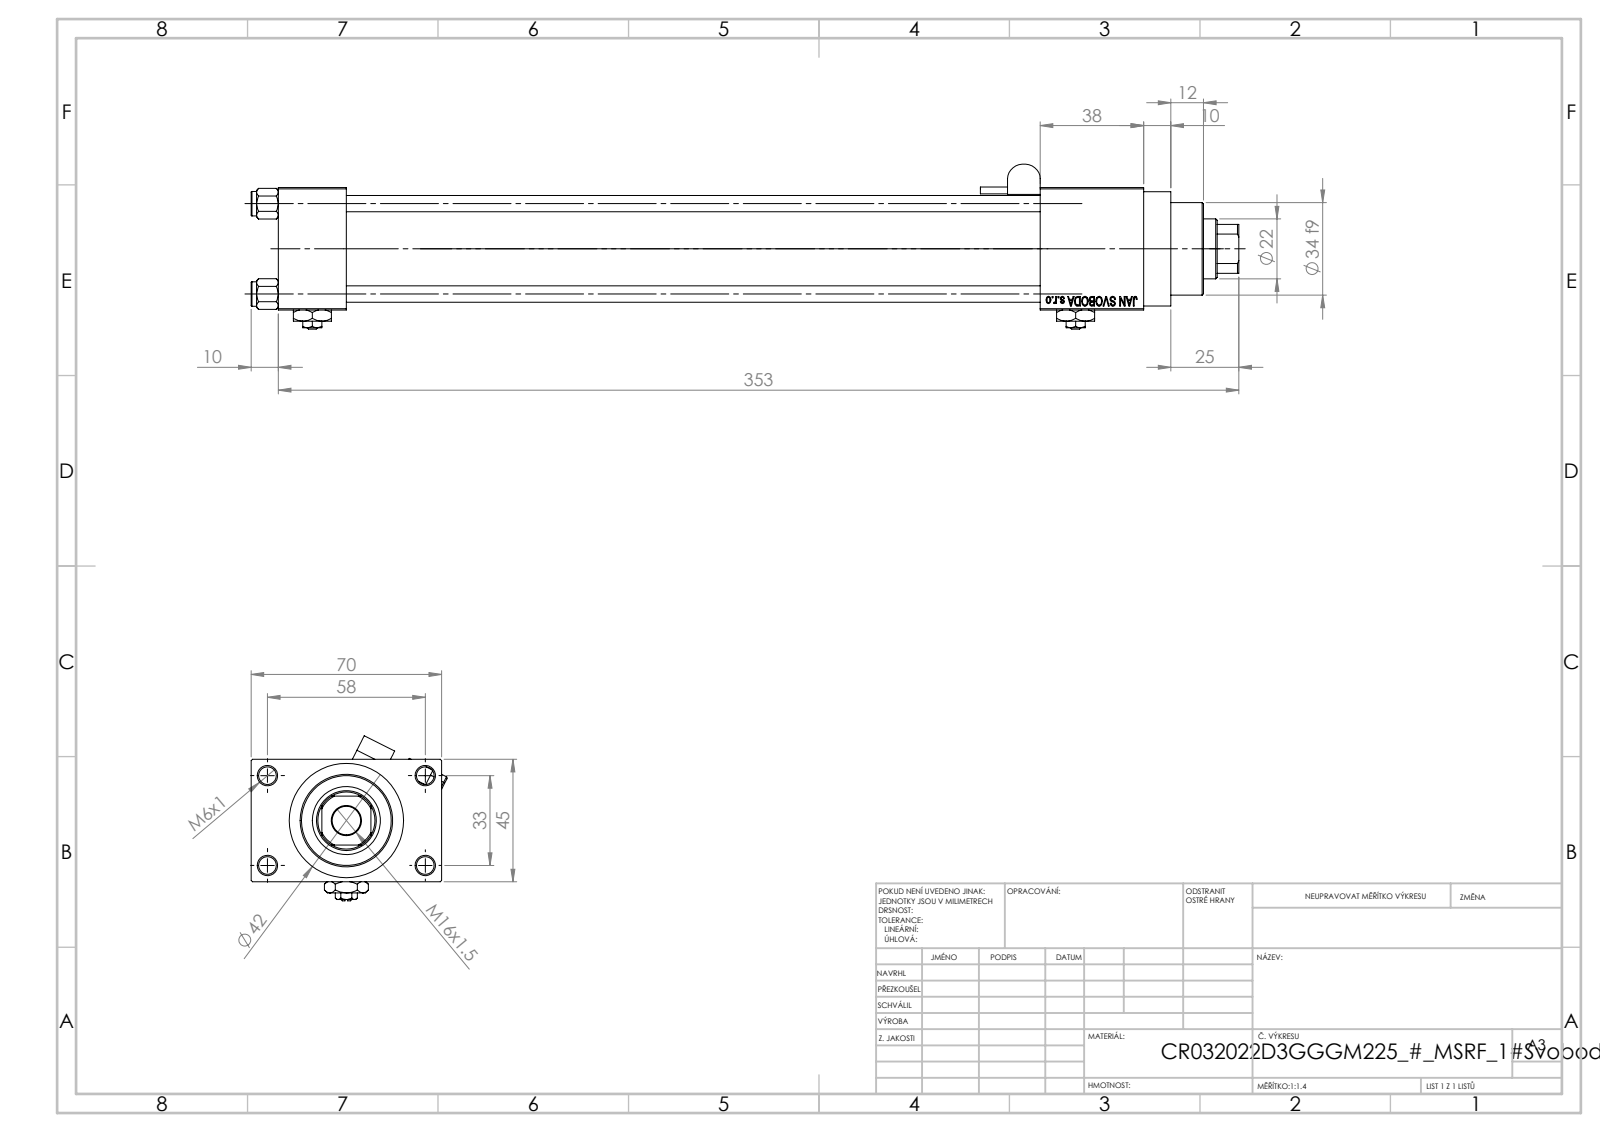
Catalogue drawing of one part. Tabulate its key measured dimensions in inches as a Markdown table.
| quantity | value |
| --- | --- |
| part name | V215_VC_A; V215CR_D_Body; MSRF_MSRG1; V215CR_VCP_D (+3 more) |
| STEP written by | SolidWorks 2019 (CONFIG_CONTROL_DESIGN) |
| units | inches |
| bodies | 14 solids, 1234 faces (560 planar, 114 cylindrical, 560 other) |
| overall size | 14.291 × 2.836 × 2.388 |
| volume | 25.36 in³ |
| surface area | 244.9 in² |
| round holes (diameter × count) | 0.236 × 4, 0.256 × 4, 0.276 × 2, 0.518 × 2, 0.787 × 2, 0.413 × 1, 0.866 × 1, 0.945 × 1, 0.984 × 1, 1.26 × 1, 1.299 × 1 |
| round bosses / shafts (diameter × count) | 0.354 × 4, 1.654 × 1, 1.496 × 1, 1.339 × 1, 0.197 × 1, 0.098 × 1 |
| partial cylindrical surfaces (radius × count) | 0.02 × 6, 0.236 × 2, 0.413 × 1 |
| main face-to-face distances | 1.772, 0.984, 0.492, 2.264, 10.039, 11.024, 11.535, 1.496, 2.756, 12.52 |
| hole center spacings | 0.488, 0.924, 1.307, 1.314, 1.392, 1.795, 2.219, 1.299 |
